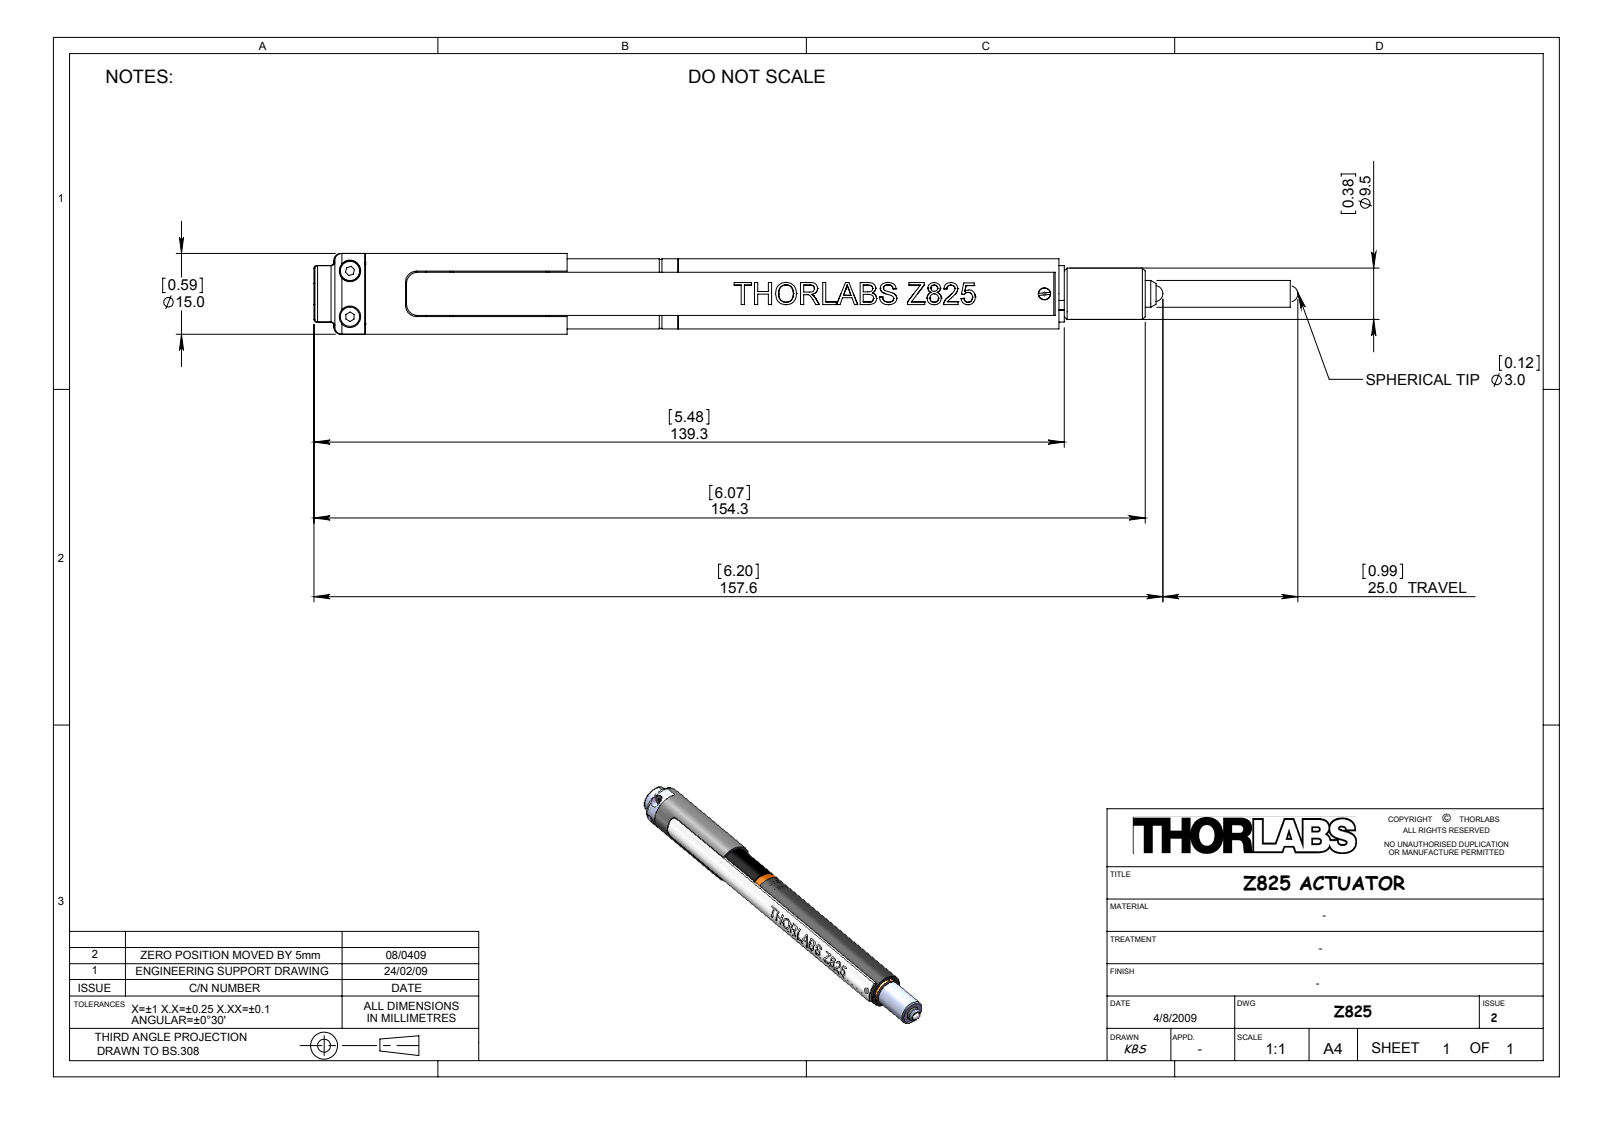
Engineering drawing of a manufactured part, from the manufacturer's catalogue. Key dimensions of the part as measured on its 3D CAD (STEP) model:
Part name (STEP PRODUCT): Z825
STEP written by: SolidWorks 2007 (AUTOMOTIVE_DESIGN)
Units: millimetres
Bodies: 0 solids, 167 faces (41 planar, 92 cylindrical, 34 other)
Overall size (bounding box): 157.59 × 15 × 15
Round holes (diameter × count): ⌀1.6 ×2, ⌀4 ×2, ⌀1.2 ×1, ⌀3.1 ×1, ⌀3.9 ×1, ⌀5.41 ×1
Round bosses / shafts (diameter × count): ⌀3.8 ×2, ⌀15 ×1, ⌀13 ×1, ⌀12.8 ×1, ⌀10.5 ×1, ⌀9.52 ×1, ⌀5 ×1, ⌀2.2 ×1
Partial cylindrical surfaces — rounded edges, fillets, slot ends (radius × count): R2 ×4, R6.55 ×1, R7.4 ×1, R7.41 ×1
Main face-to-face distances: 8, 8.2, 1, 15, 128.81, 129.81, 144.81, 16, 37.51, 91.3
Hole centre spacings: 8.5, 128.98, 129.17
